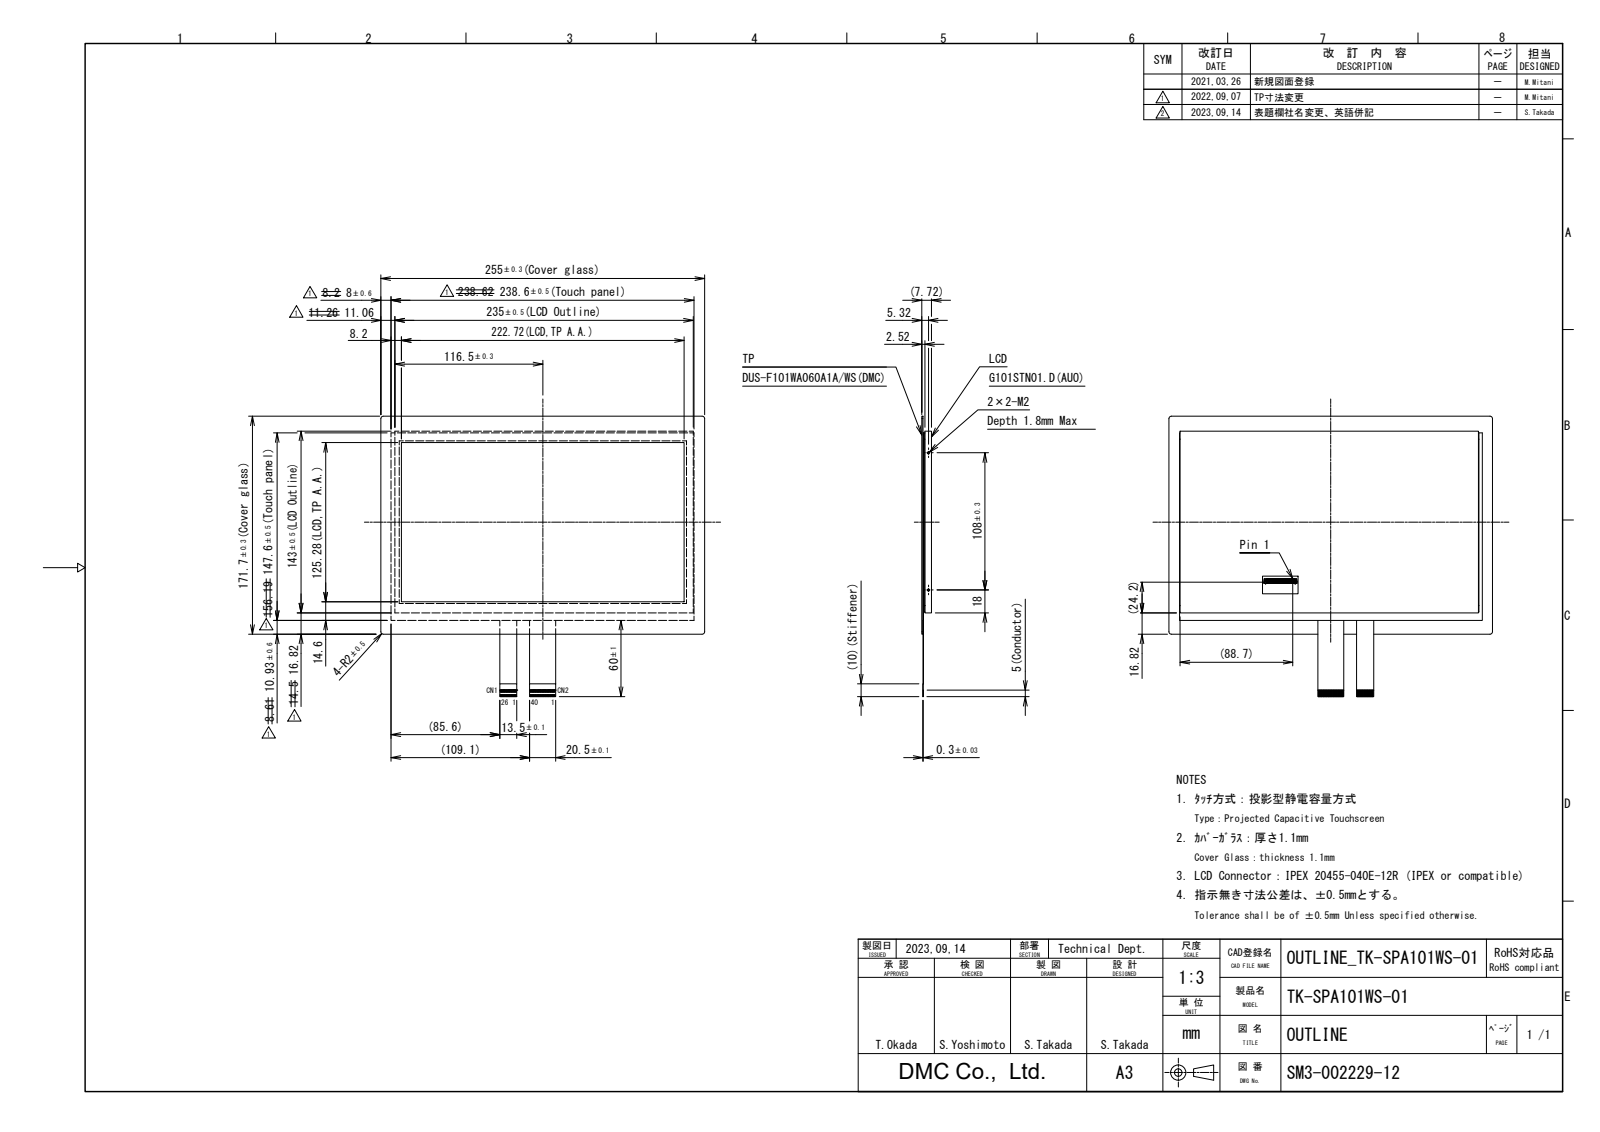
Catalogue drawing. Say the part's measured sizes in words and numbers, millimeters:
The part is named "TK-SPA101WS-01_3D". Its 3-D file was written by "Autodesk Inventor 2020 (AUTOMOTIVE_DESIGN)". It is 1 solid with 1920 faces: 1359 planar, 513 cylindrical and 48 other. Overall it measures 255 by 220.77 by 7.72 millimeters. Its volume is 236 814 cubic millimeters and its surface area 160 223 square millimeters. Round holes: 2 of diameter 0.5, 2 of diameter 1.57. Partial cylindrical surfaces (rounded edges, fillets, slot ends): 44 of radius 0.1, 16 of radius 0.17, 9 of radius 0.15, 9 of radius 0.2, 6 of radius 0.3, 4 of radius 2, 2 of radius 0.14, 2 of radius 0.22. The main face-to-face distances are 7.72, 1.4, 6.32, 5.2, 1.12, 2.52, 1.42, 6.62, 1.1, 1.37. The hole center spacings are 25.37, 108.
